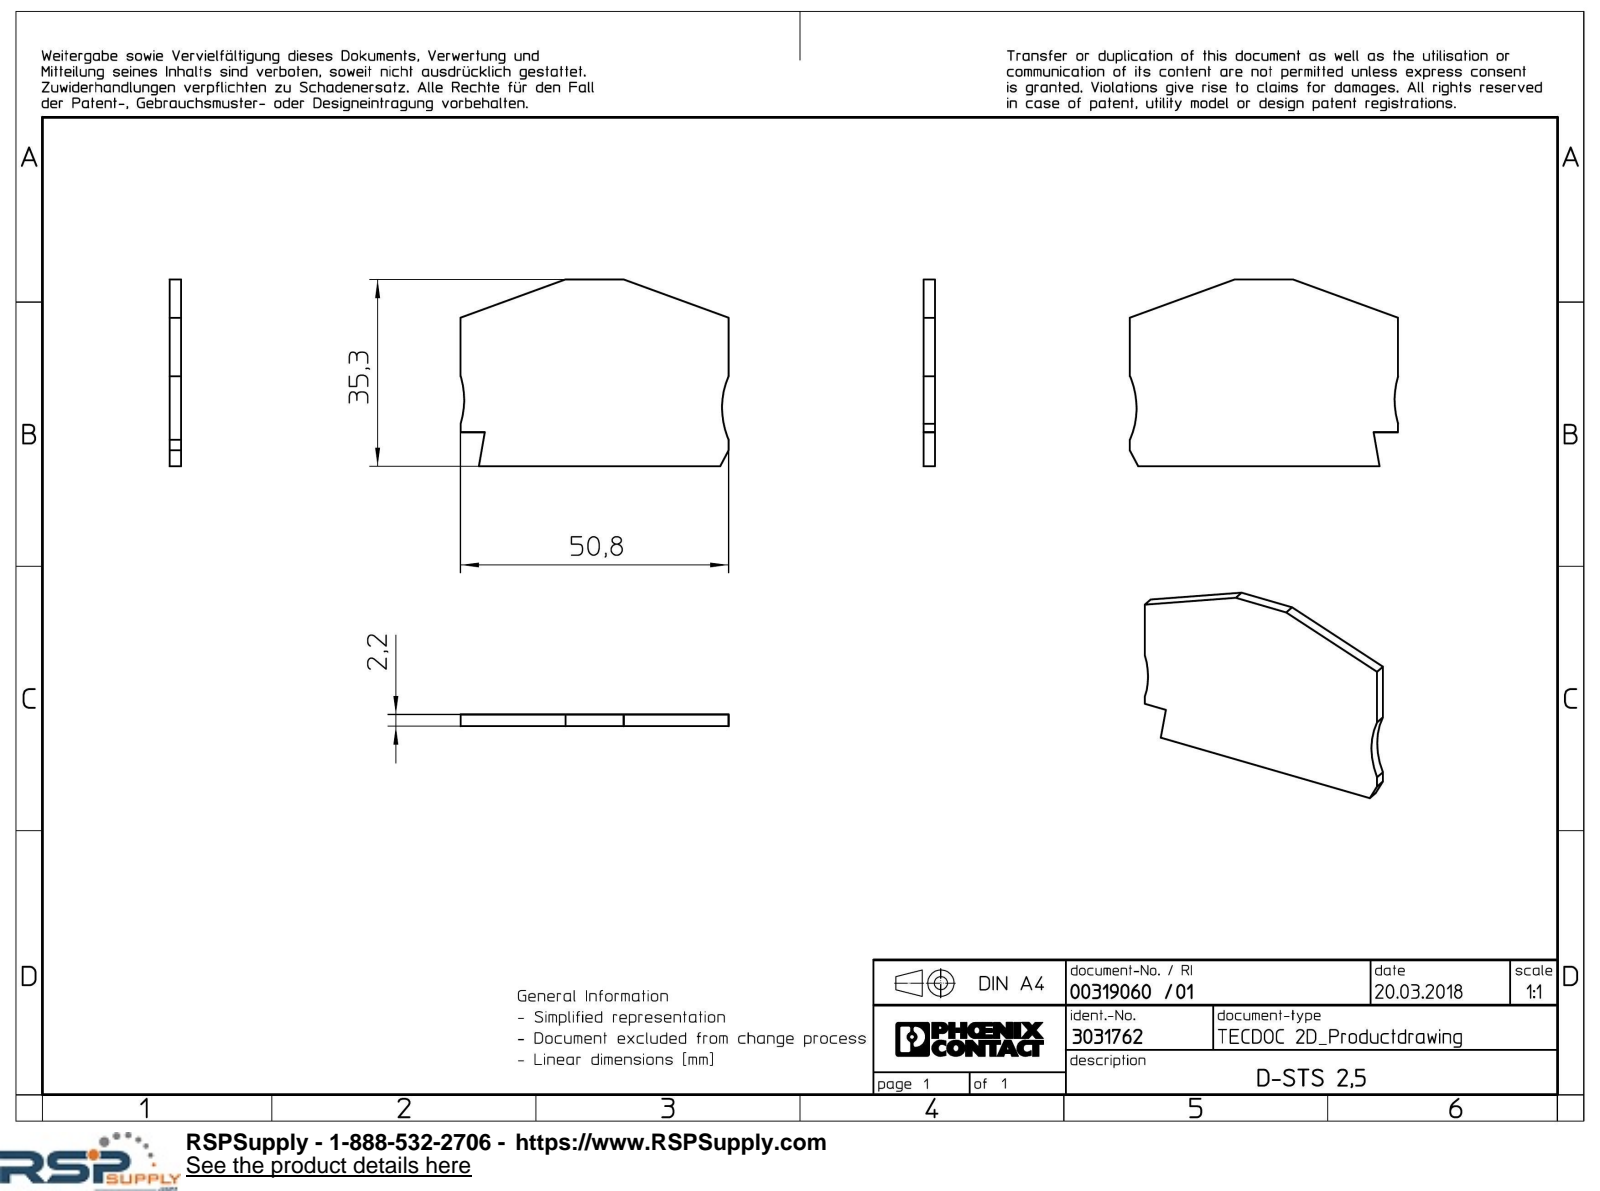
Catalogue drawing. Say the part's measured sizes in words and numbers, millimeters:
The part is named "d-sts_25-select". Its 3-D file was written by "Creo Elements/Direct Modeling 18.1I 14-Aug-2016 (C) Parametric Technology GmbH (AUTOMOTIVE_DESIGN)". It is 1 solid with 15 faces: 13 planar, 2 cylindrical and 0 other. Overall it measures 50.8 by 35.3 by 2.2 millimeters. Its volume is 3 535 cubic millimeters and its surface area 3 567 square millimeters. Partial cylindrical surfaces (rounded edges, fillets, slot ends): 2 of radius 15. The main face-to-face distances are 2.2, 50.8, 35.3, 6.4, 28.9.
